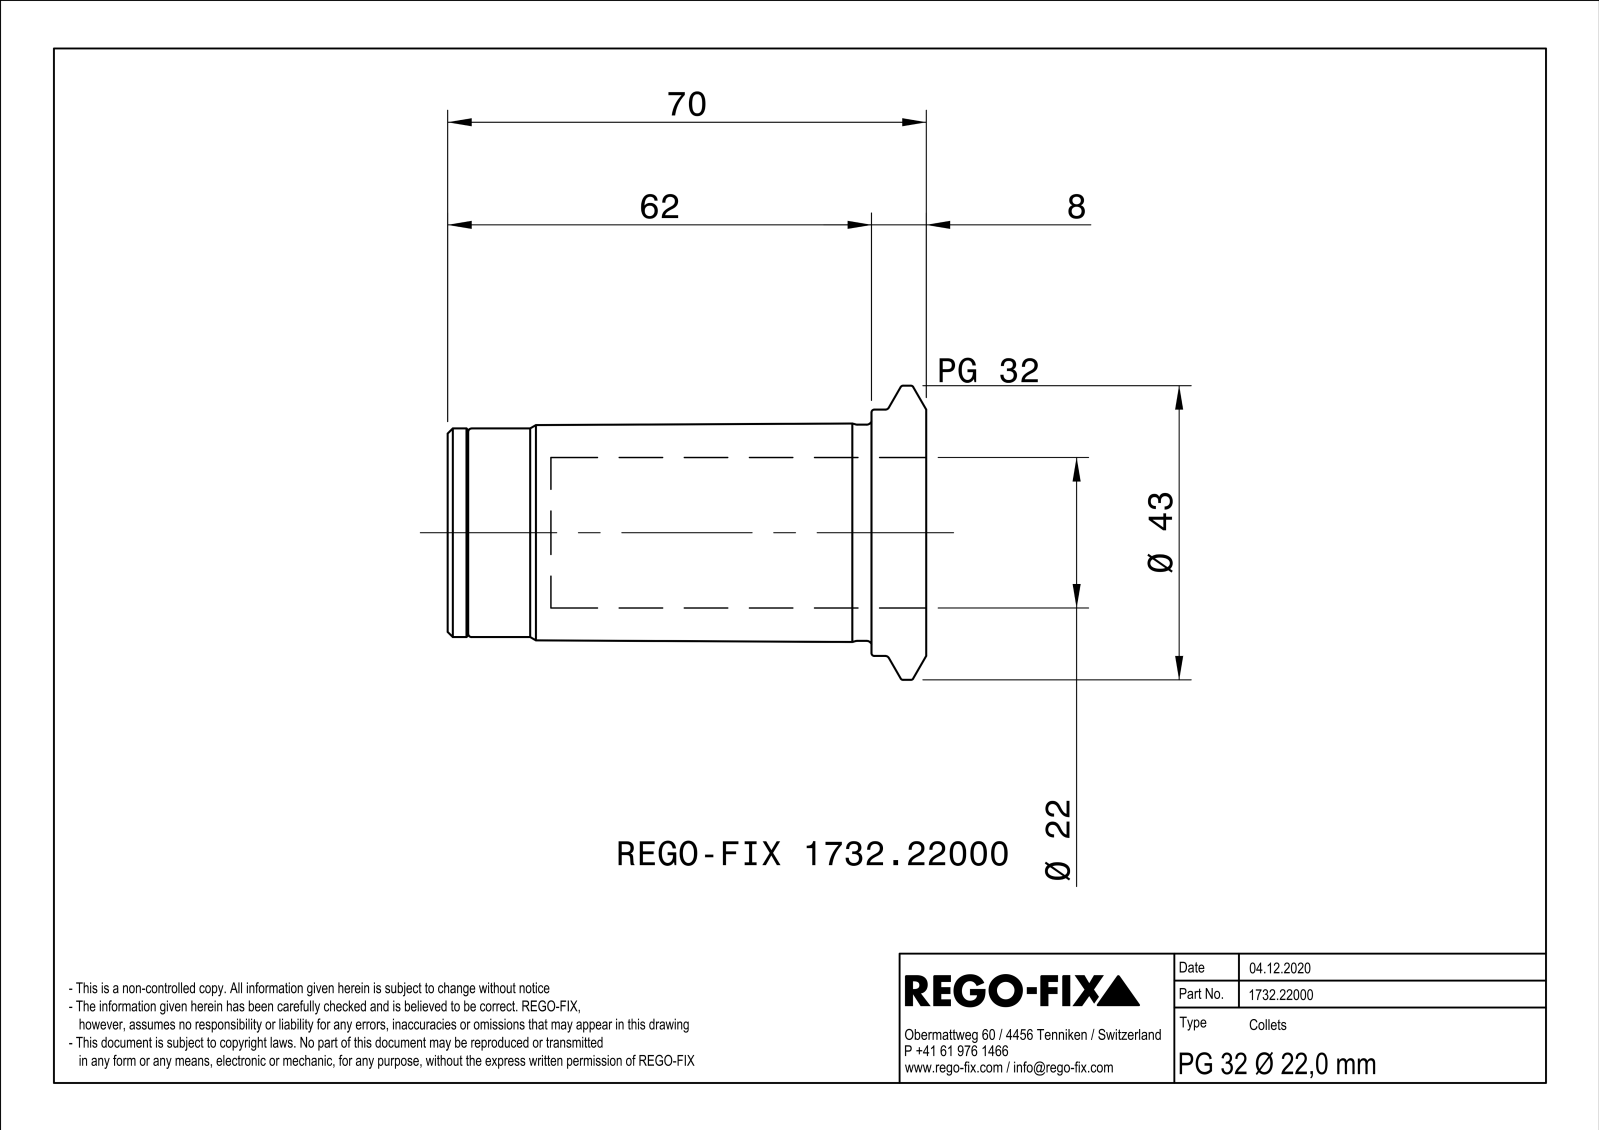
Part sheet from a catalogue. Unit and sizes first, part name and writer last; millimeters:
Units: millimetres
Overall size (bounding box): 70 × 43 × 42.99
Round holes (diameter × count): ⌀7.95 ×1, ⌀8.92 ×1, ⌀10.5 ×1, ⌀22 ×1, ⌀26.92 ×1, ⌀28.5 ×1
Round bosses / shafts (diameter × count): ⌀43 ×1, ⌀36 ×1, ⌀31.6 ×1, ⌀30.5 ×1, ⌀26.5 ×1, ⌀21 ×1
Main face-to-face distances: 1, 70, 58, 12, 59, 11, 8, 50, 51, 62
Volume: 33 254 mm³ · Surface area: 16 103 mm²
Bodies: 1 solid, 81 faces (22 planar, 20 cylindrical, 39 other)
Part name (STEP PRODUCT): NOCUT
STEP written by: SIEMENS PLM Software Solid Edge ST10 (AUTOMOTIVE_DESIGN)
